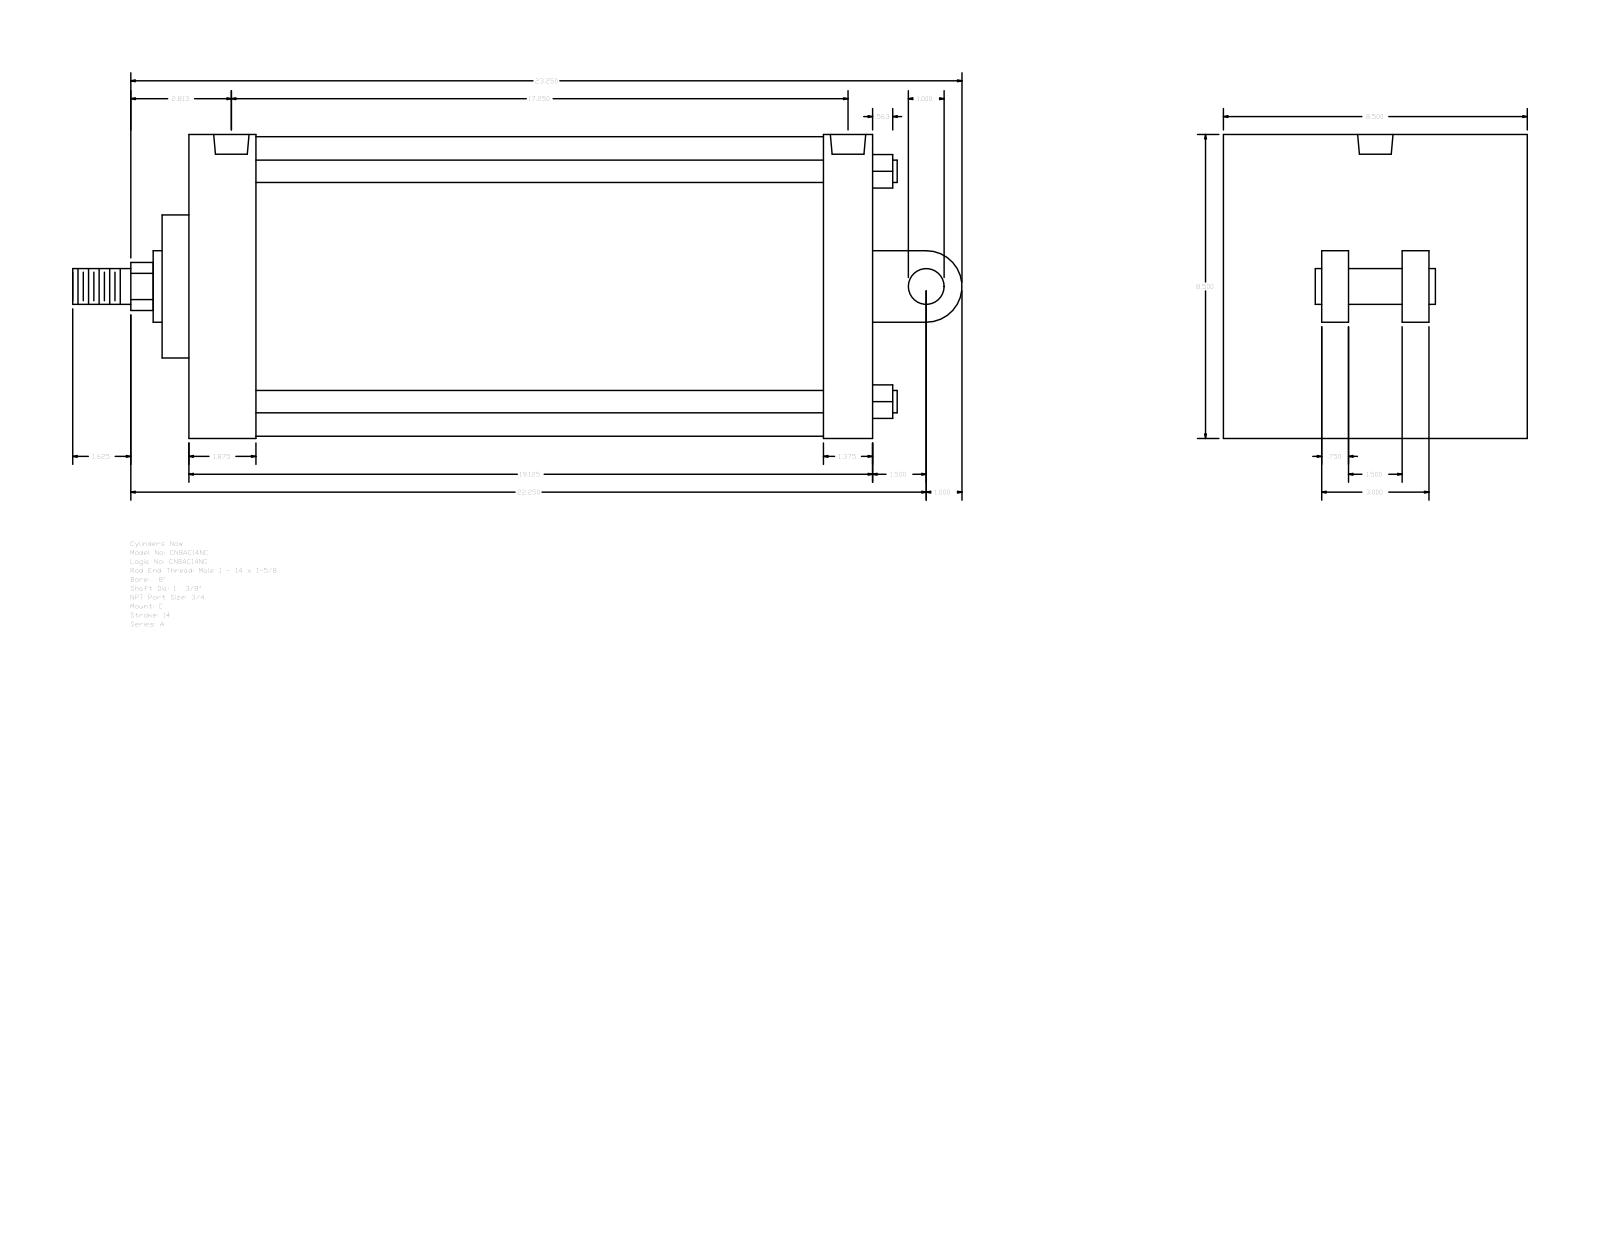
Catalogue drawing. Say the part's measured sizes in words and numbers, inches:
The part is named "A_C__0800_1.375". Its 3-D file was written by "GSSL Pune (CONFIG_CONTROL_DESIGN)". It is 0 solids with 104 faces: 75 planar, 29 cylindrical and 0 other. Overall it measures 24.875 by 8.5 by 8.5 inches. Round holes: 4 of diameter 0.594, 2 of diameter 0.989. Round bosses or shafts: 4 of diameter 0.625, 2 of diameter 1, 1 of diameter 8.375, 1 of diameter 2, 1 of diameter 1.375. Partial cylindrical surfaces (rounded edges, fillets, slot ends): 1 of radius 0.672, 1 of radius 1. The main face-to-face distances are 19.125, 8.5, 2.25, 1.875, 17.25, 17.75, 15.875, 1.375, 3.5, 2.75. The hole center spacings are 0.25, 16.75, 17, 17.25.
